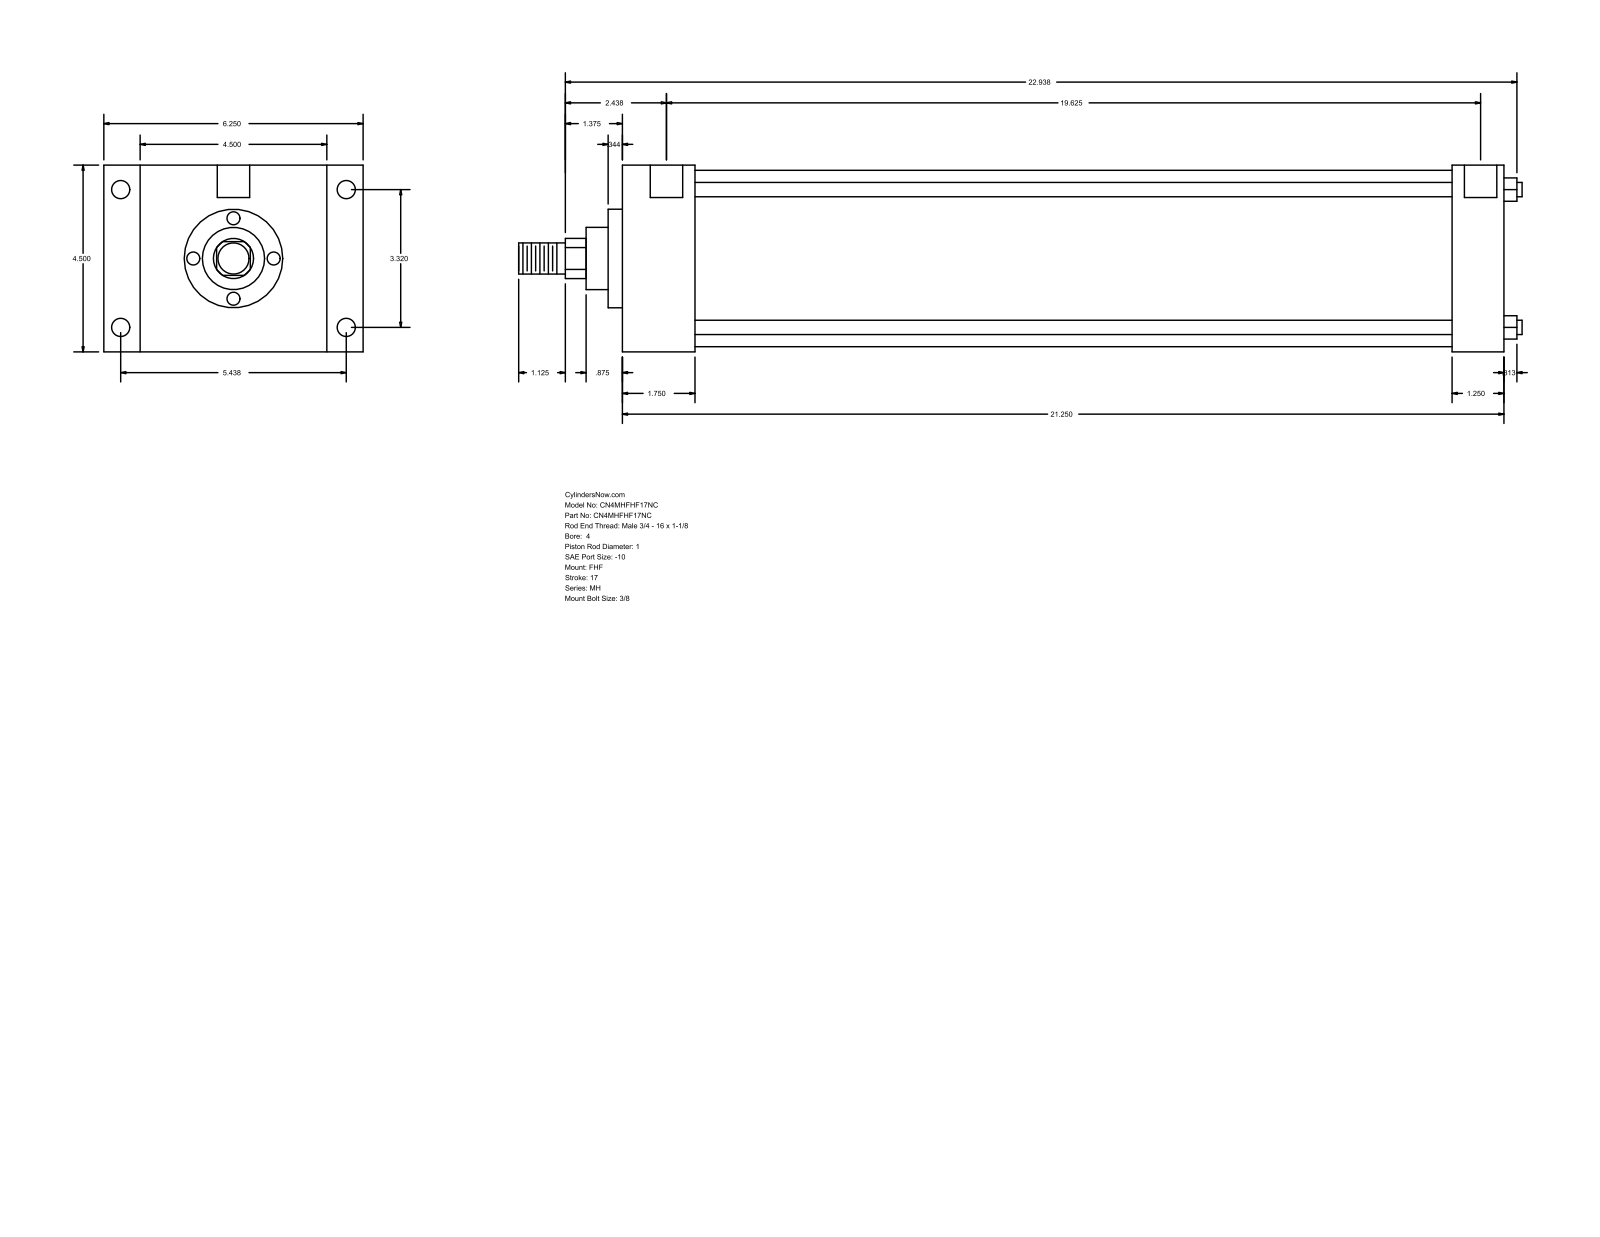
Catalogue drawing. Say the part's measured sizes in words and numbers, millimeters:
The part is named "MH_FHF__0400_1". Its 3-D file was written by "GSSL Pune (CONFIG_CONTROL_DESIGN)". It is 0 solids with 90 faces: 61 planar, 29 cylindrical and 0 other. Overall it measures 614.36 by 158.75 by 114.3 millimeters. Round holes: 4 of diameter 8.73, 4 of diameter 11.13, 2 of diameter 19.84. Round bosses or shafts: 4 of diameter 8.76, 1 of diameter 107.95, 1 of diameter 60.33, 1 of diameter 38.1, 1 of diameter 25.4, 1 of diameter 19.05. Partial cylindrical surfaces (rounded edges, fillets, slot ends): 1 of radius 12.29. The main face-to-face distances are 114.3, 539.75, 44.46, 495.29, 22.23, 136.53, 158.76, 508, 463.54, 31.75. The hole center spacings are 84.32, 138.12, 161.82, 501.65, 1.58, 1.59, 498.48, 500.06.
